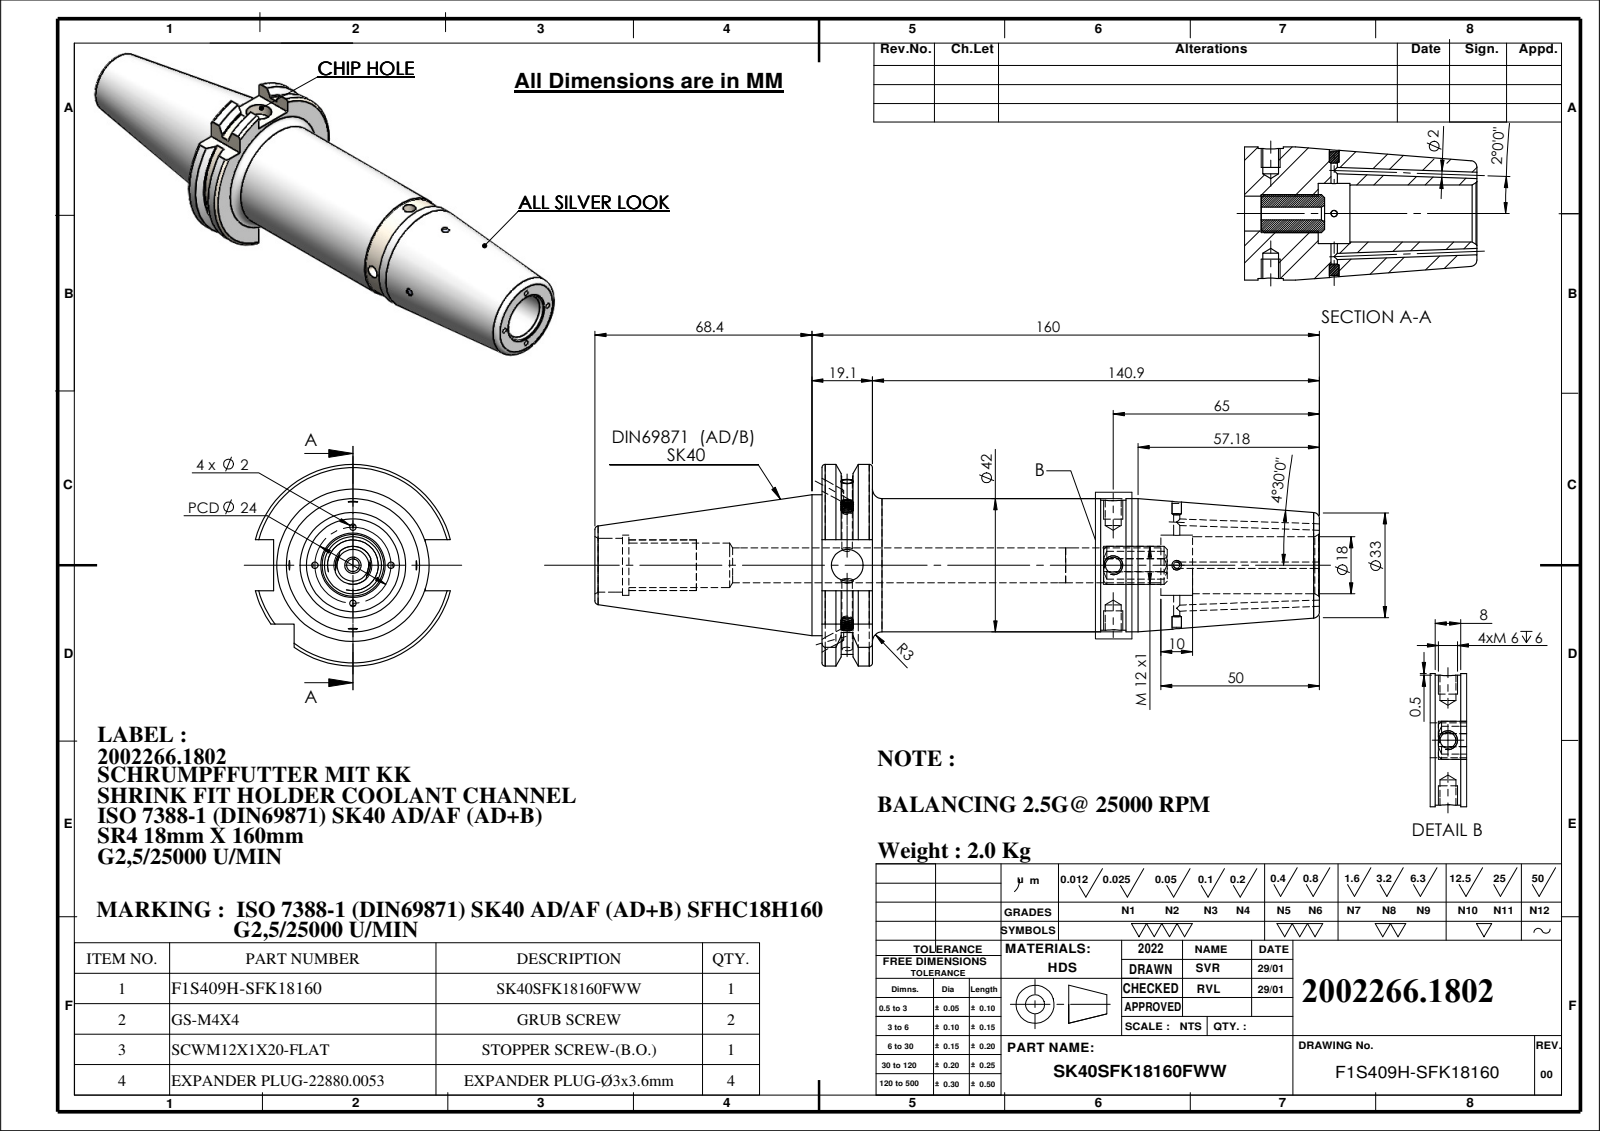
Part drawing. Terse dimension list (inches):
name: 91406-SR418160; SK40SFK18160FWW; EXPANDER PLUG Ø3x3.6; SCWM12X1X20-FLAT (+1 more)
written by: SolidWorks 2018 (CONFIG_CONTROL_DESIGN)
unit: in
bodies: 8 solids, 304 faces (63 planar, 113 cylindrical, 128 other)
size: 8.992 × 2.502 × 2.42
volume: 15.8 in³; area: 73.68 in²
holes: 6× ⌀0.079, 2× ⌀0.118, 2× ⌀0.197, 1× ⌀0.13, 1× ⌀0.157, 1× ⌀0.394, 1× ⌀0.433, 1× ⌀0.433, 1× ⌀0.551, 1× ⌀0.669, 1× ⌀0.708, 1× ⌀0.748
bosses: 2× ⌀0.157, 1× ⌀1.75, 1× ⌀1.654, 1× ⌀1.614
rounds: 1× R0.236, 1× R1.107, 1× R1.251
face distances: 0.626, 6.173, 5.547, 4.205, 3.579, 1.969, 0.634, 1.882, 0.394, 2.819
hole spacings: 0.787, 3.301, 4.089
